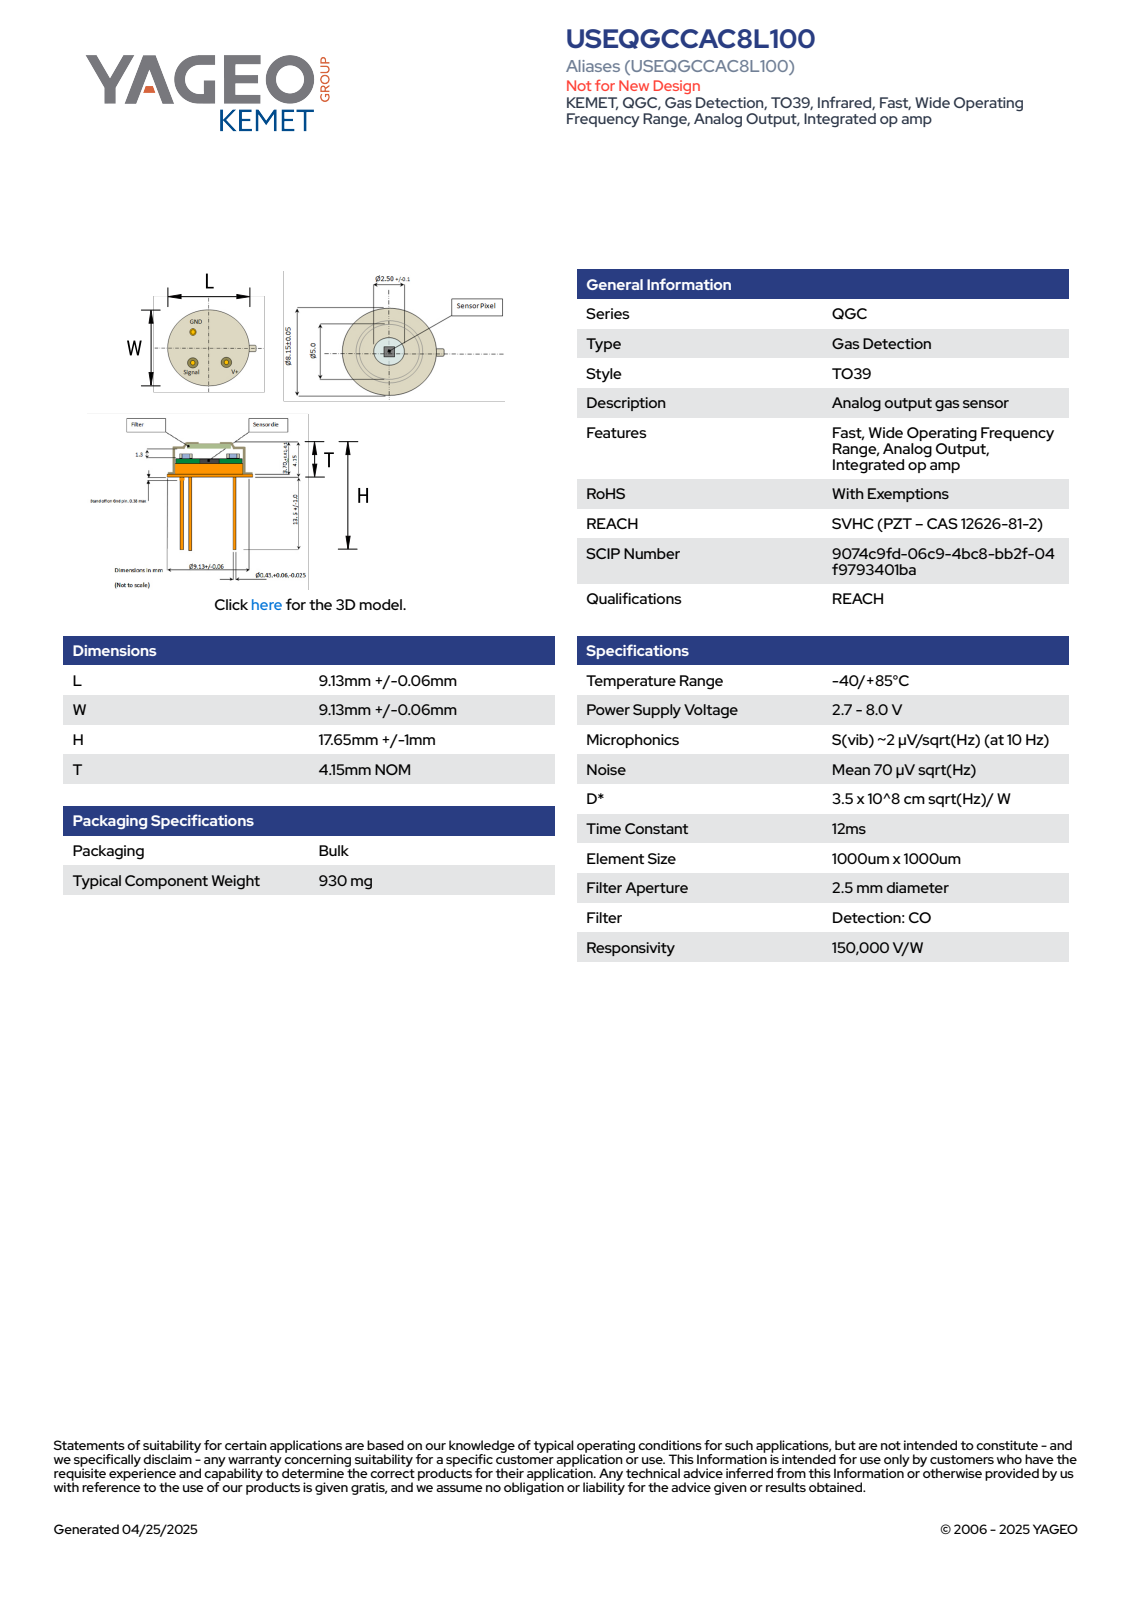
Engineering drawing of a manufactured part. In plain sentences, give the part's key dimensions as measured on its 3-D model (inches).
The part is named "SF_QGCS_L9.19W9.19H18.65T4.15". Its 3-D file was written by "SolidWorks 2014 (AUTOMOTIVE_DESIGN)". It is 1 solid with 82 faces: 66 planar, 14 cylindrical and 2 other. Overall it measures 0.734 by 0.377 by 0.362 inches. Its volume is 0.014 cubic inches and its surface area 0.473 square inches. Round holes: 1 of diameter 0.098. Round bosses or shafts: 3 of diameter 0.019, 1 of diameter 0.362, 1 of diameter 0.323. The main face-to-face distances are 0.156, 0.163, 0.138, 0.018, 0.146, 0.571, 0.589, 0.726, 0.734, 0.727.
